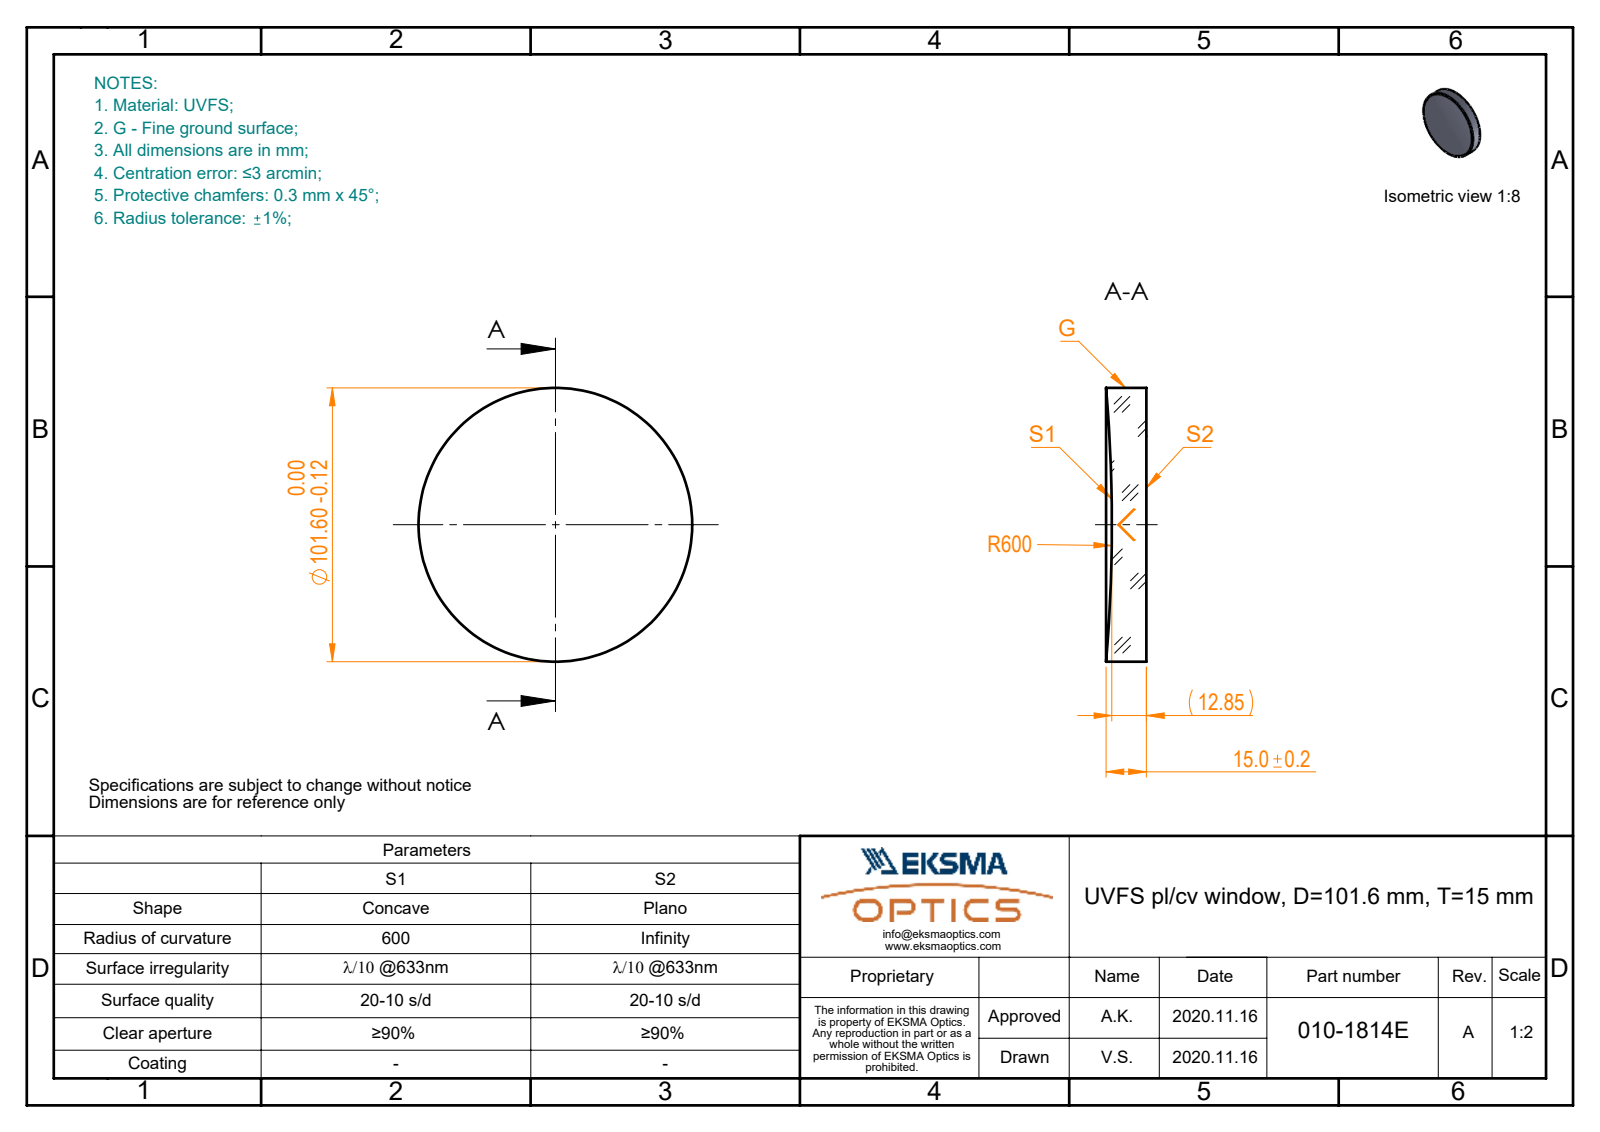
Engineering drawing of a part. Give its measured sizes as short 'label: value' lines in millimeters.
name: 010-1814E_UVFS_PCV_window
written by: SolidWorks 2019 (CONFIG_CONTROL_DESIGN)
unit: mm
bodies: 1 solid, 5 faces (1 planar, 2 cylindrical, 2 other)
size: 101.6 × 101.6 × 15
volume: 112 871 mm³; area: 21 017 mm²
bosses: 1× ⌀101.6
